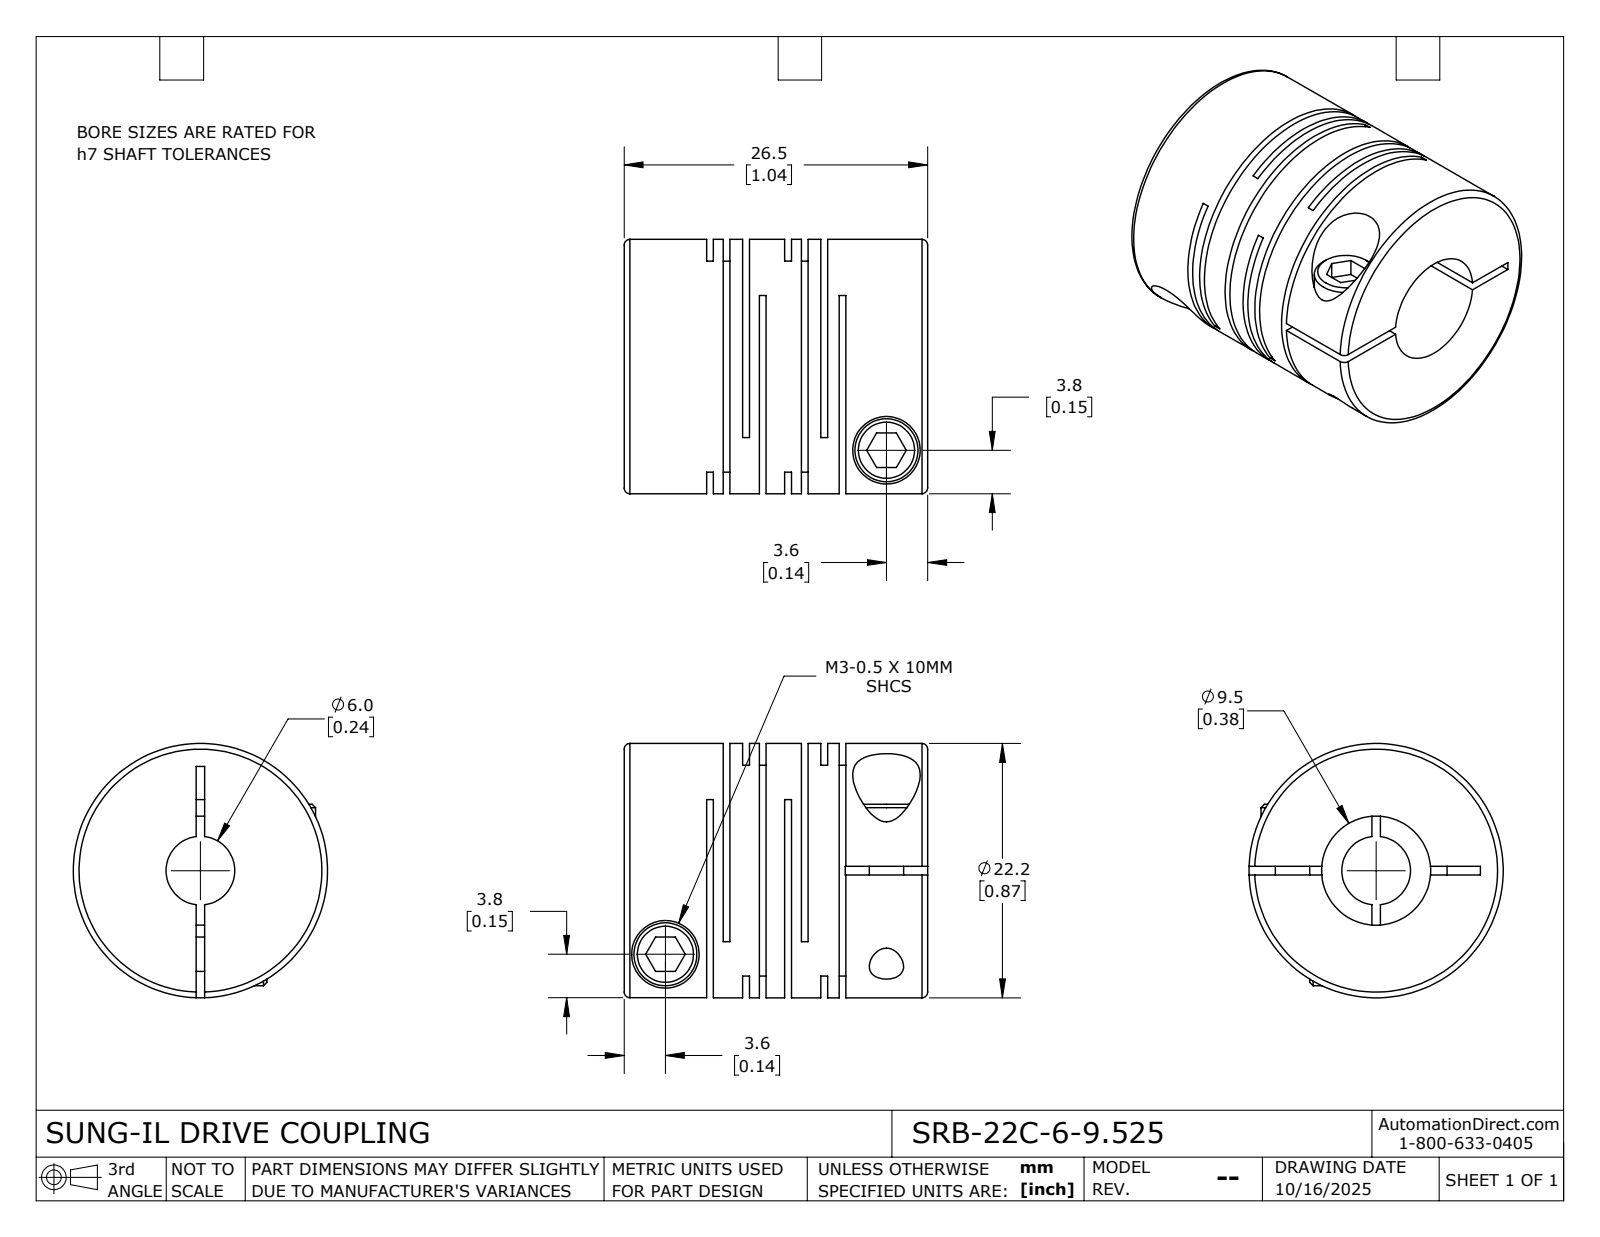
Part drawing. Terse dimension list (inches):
name: SRB-22C-6-9.525
written by: SolidWorks 2024 (CONFIG_CONTROL_DESIGN)
unit: in
bodies: 1 solid, 115 faces (60 planar, 42 cylindrical, 13 other)
size: 1.043 × 0.874 × 0.874
volume: 0.437 in³; area: 11.75 in²
holes: 2× ⌀0.118, 2× ⌀0.232, 1× ⌀0.236, 1× ⌀0.375
bosses: 2× ⌀0.217, 1× ⌀0.874
face distances: 0.023, 0.269, 0.057, 0.124, 0.211, 0.144, 0.067, 0.292, 0.245, 0.08
